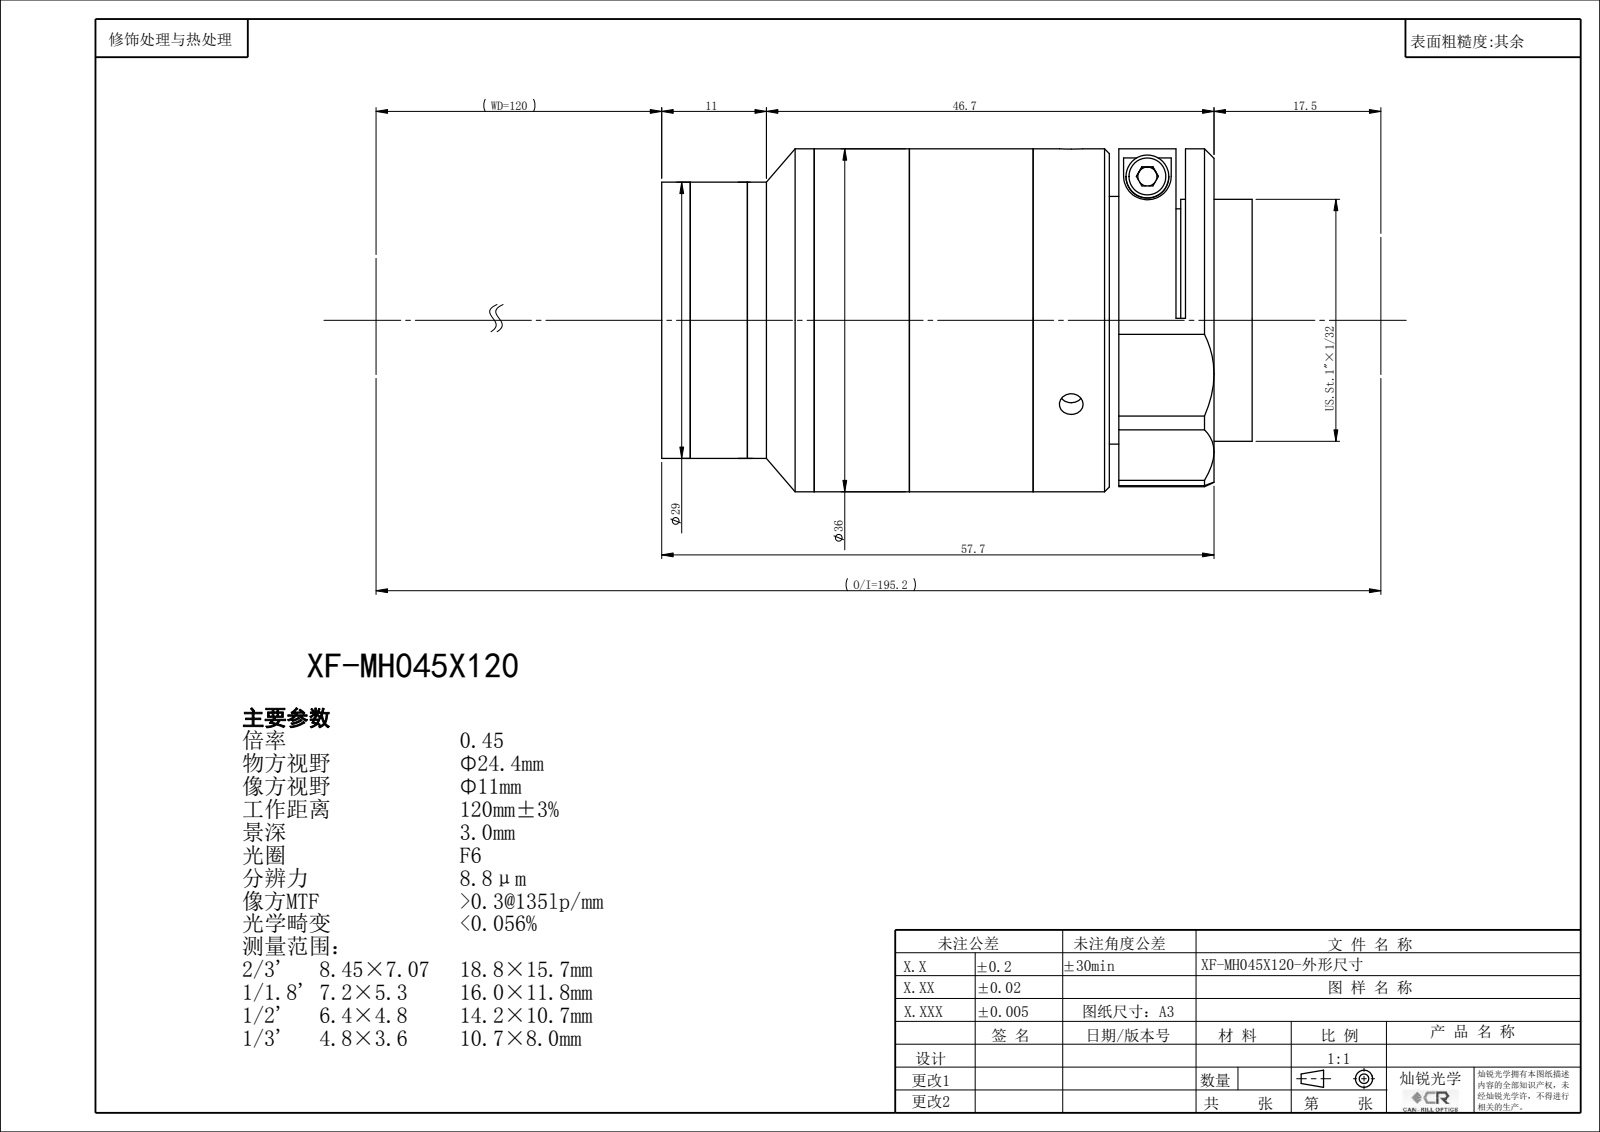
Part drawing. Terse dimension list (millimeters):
name: XF-MH045X120
written by: SolidWorks 2022 (CONFIG_CONTROL_DESIGN)
unit: mm
bodies: 0 solids, 131 faces (67 planar, 42 cylindrical, 22 other)
size: 61.81 × 36.03 × 36
holes: 3× ⌀2.5, 1× ⌀14, 1× ⌀22.4, 1× ⌀24, 1× ⌀24.9, 1× ⌀26.4, 1× ⌀27
bosses: 1× ⌀36, 1× ⌀34, 1× ⌀29, 1× ⌀25.4
face distances: 18.79, 35.22, 54.01, 1.5, 52.51, 17.29, 12.22, 23, 40.29, 41.79
